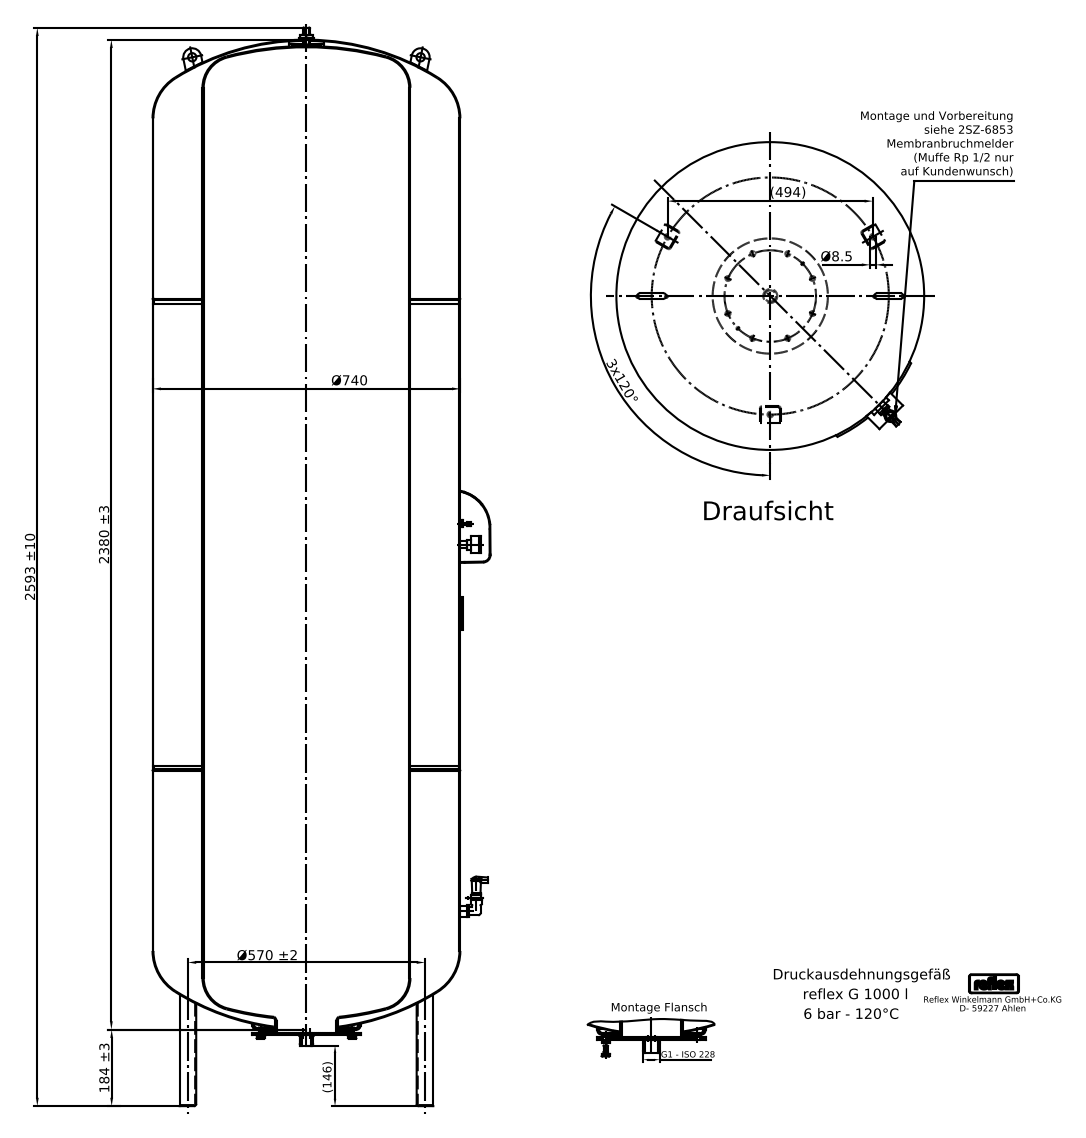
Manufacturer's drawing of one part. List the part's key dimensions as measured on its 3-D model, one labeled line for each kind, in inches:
STEP written by: Mechanical Desktop 2008 (CONFIG_CONTROL_DESIGN)
Units: inches
Bodies: 22 solids, 434 faces (212 planar, 138 cylindrical, 84 other)
Overall size (bounding box): 102.087 × 31.969 × 29.179
Volume: 59 210 in³ · Surface area: 12 950 in²
Round holes (diameter × count): ⌀0.394 ×1, ⌀6.339 ×1, ⌀9.843 ×1
Round bosses / shafts (diameter × count): ⌀0.394 ×9, ⌀0.787 ×3, ⌀1.102 ×2, ⌀1.024 ×2, ⌀0.945 ×2, ⌀29.134 ×1, ⌀10.236 ×1, ⌀9.055 ×1
Partial cylindrical surfaces — rounded edges, fillets, slot ends (radius × count): R0.984 ×18, R0.155 ×4, R0.062 ×3, R0.354 ×3, R0.106 ×2, R0.186 ×2, R0.256 ×2, R0.259 ×2
Main face-to-face distances: 78.819, 0.236, 7.717, 86.535, 7.953, 86.772, 6.732, 0.197, 0.231, 0.699
Hole centre spacings: 15.177
